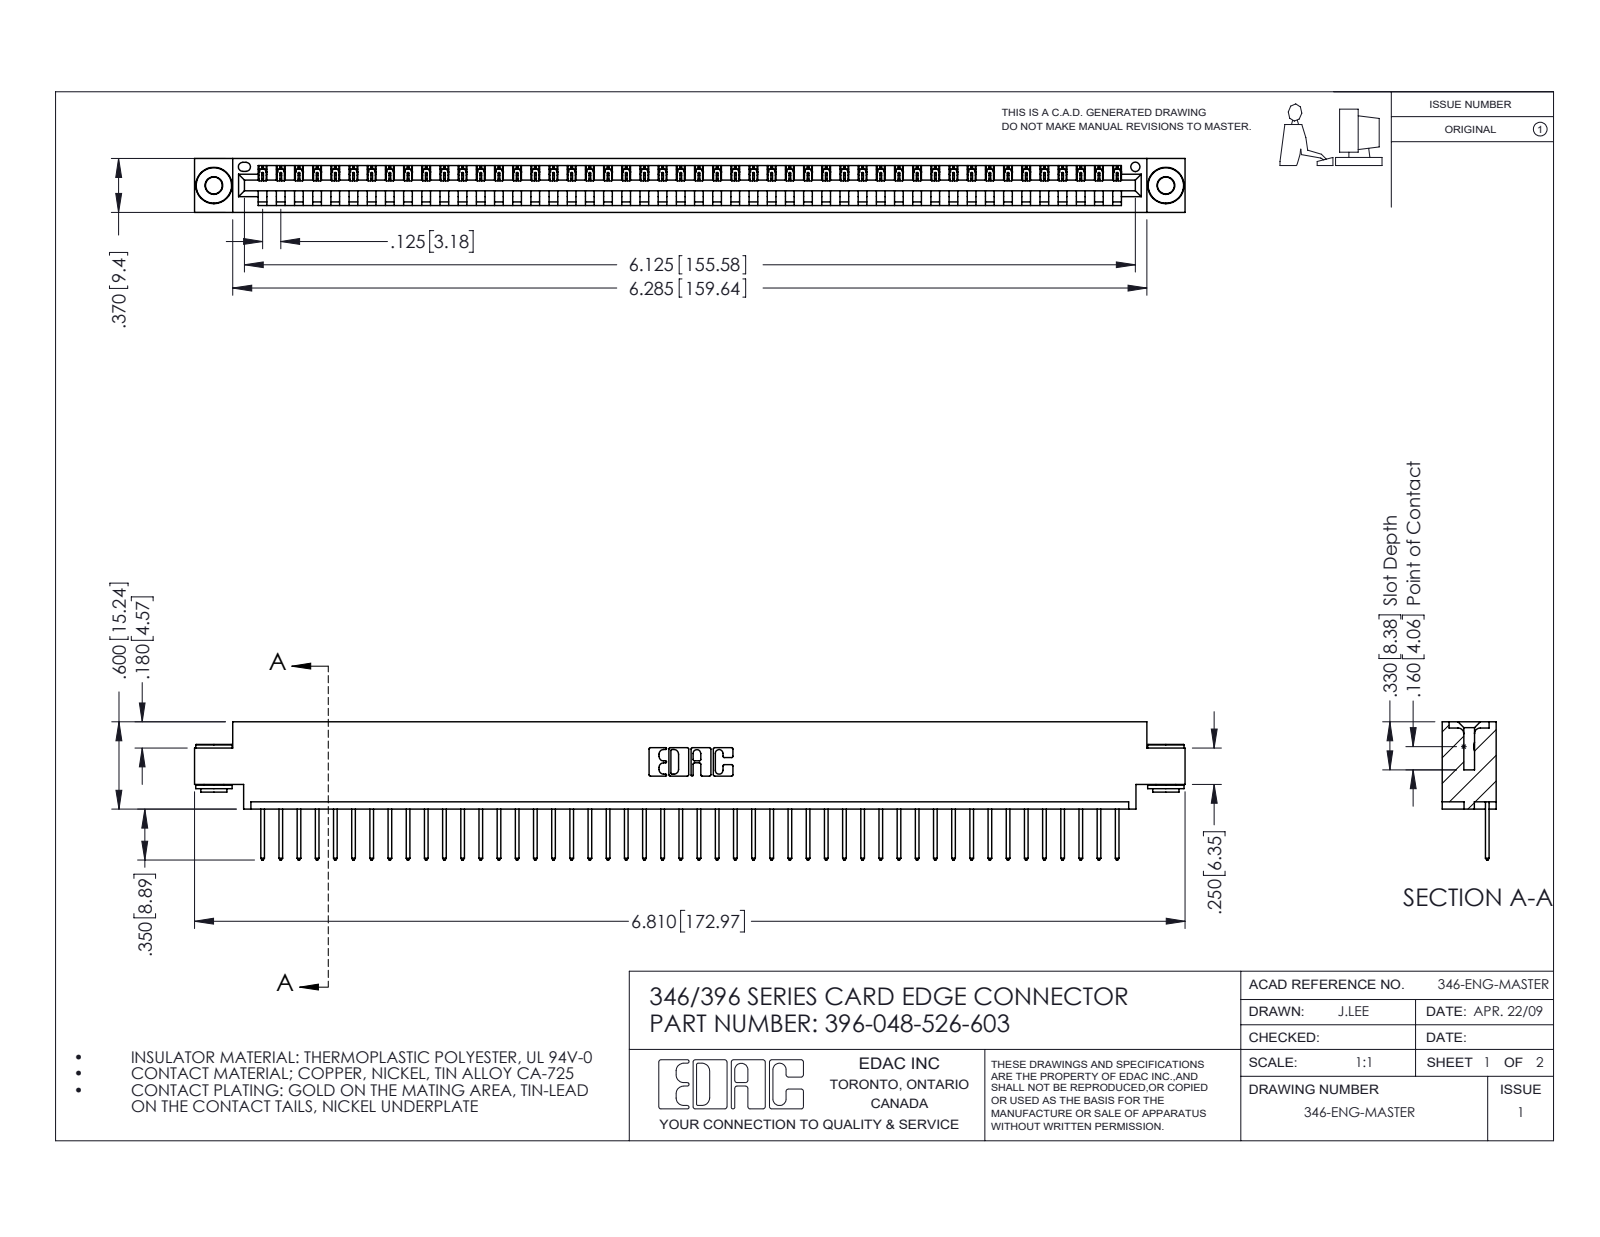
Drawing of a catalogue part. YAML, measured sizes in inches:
part_name: "346 Part_0.170 Offset - 0.156 Dia-TH; 396-048-526-603; 345-250-002_345-250-002-102; 345-292-001_345-293-126"
step_written_by: "SolidWorks 2016 (CONFIG_CONTROL_DESIGN)"
units: inches
bodies: {solids: 51, faces: 2948, planar: 2010, cylindrical: 930, other: 8}
overall_size: [6.81, 0.95, 0.37]
volume: 1.002
surface_area: 32.44
round_holes:
  - {diameter: 0.116, count: 2}
  - {diameter: 0.156, count: 2}
  - {diameter: 0.064, count: 1}
round_bosses_or_shafts:
  - {diameter: 0.25, count: 2}
  - {diameter: 0.18, count: 2}
  - {diameter: 0.136, count: 2}
partial_cylinders:
  - {radius: 0.006, count: 96}
  - {radius: 0.01, count: 96}
  - {radius: 0.01, count: 22}
  - {radius: 0.007, count: 6}
  - {radius: 0.031, count: 6}
  - {radius: 0.026, count: 3}
  - {radius: 0.031, count: 2}
  - {radius: 0.04, count: 2}
face_to_face_distances: [0.048, 0.322, 0.37, 0.25, 0.025, 0.072, 0.298, 0.148, 0.222, 0.1]
hole_center_spacings: [0.246, 6.336, 6.545]
